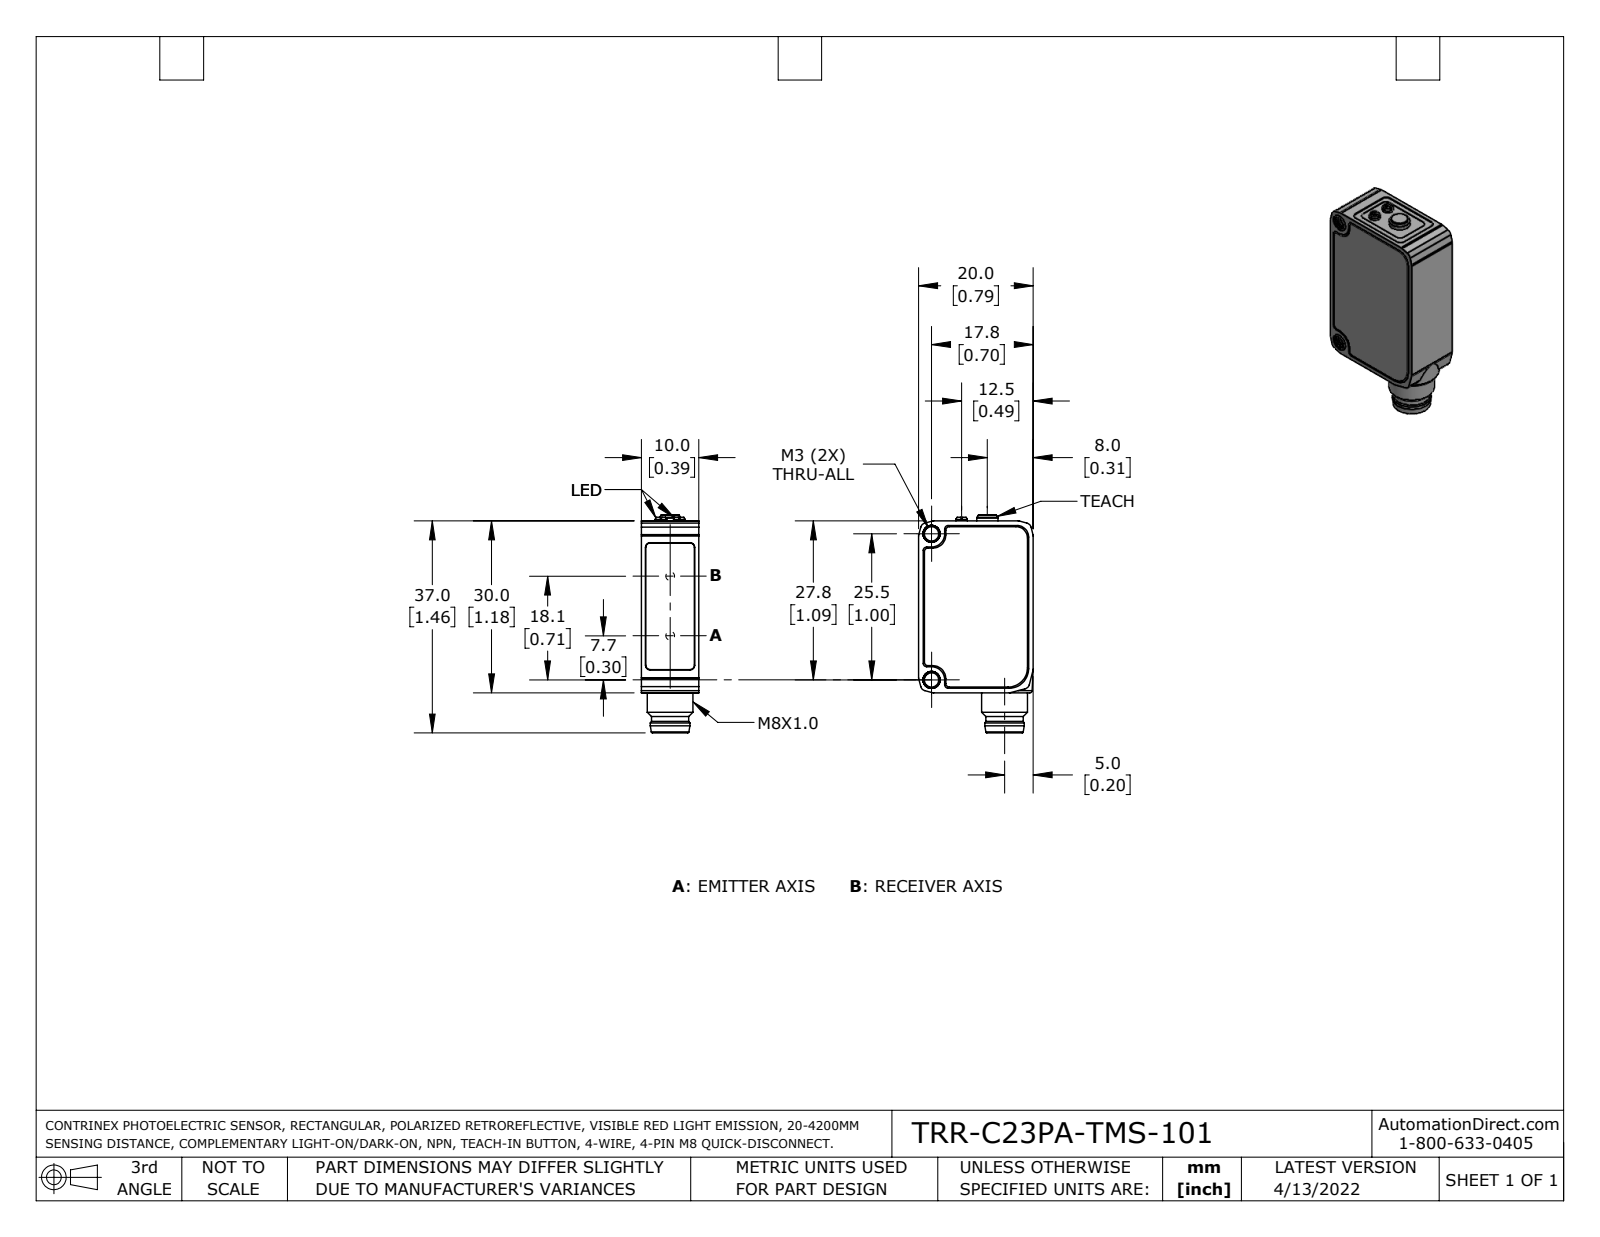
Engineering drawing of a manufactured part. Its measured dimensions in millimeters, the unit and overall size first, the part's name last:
Units: millimetres
Overall size (bounding box): 38 × 20 × 10
Round holes (diameter × count): ⌀2.5 ×2, ⌀3.6 ×2, ⌀5.8 ×1
Round bosses / shafts (diameter × count): ⌀1 ×4, ⌀2 ×2, ⌀8 ×1, ⌀6.9 ×1, ⌀6.5 ×1, ⌀3.7 ×1
Partial cylindrical surfaces — rounded edges, fillets, slot ends (radius × count): R0.8 ×20, R1 ×11, R0.6 ×8, R2.3 ×4, R2 ×2, R3.4 ×2
Main face-to-face distances: 10, 19.9, 20, 29.9, 30, 29.9, 0.7, 0.8, 0.8, 1
Hole centre spacings: 25.5
Volume: 5 960 mm³ · Surface area: 2 823 mm²
Bodies: 1 solid, 279 faces (88 planar, 137 cylindrical, 54 other)
Part name (STEP PRODUCT): TRR-C23PA-TMS-101
STEP written by: SolidWorks 2021 (AUTOMOTIVE_DESIGN)
